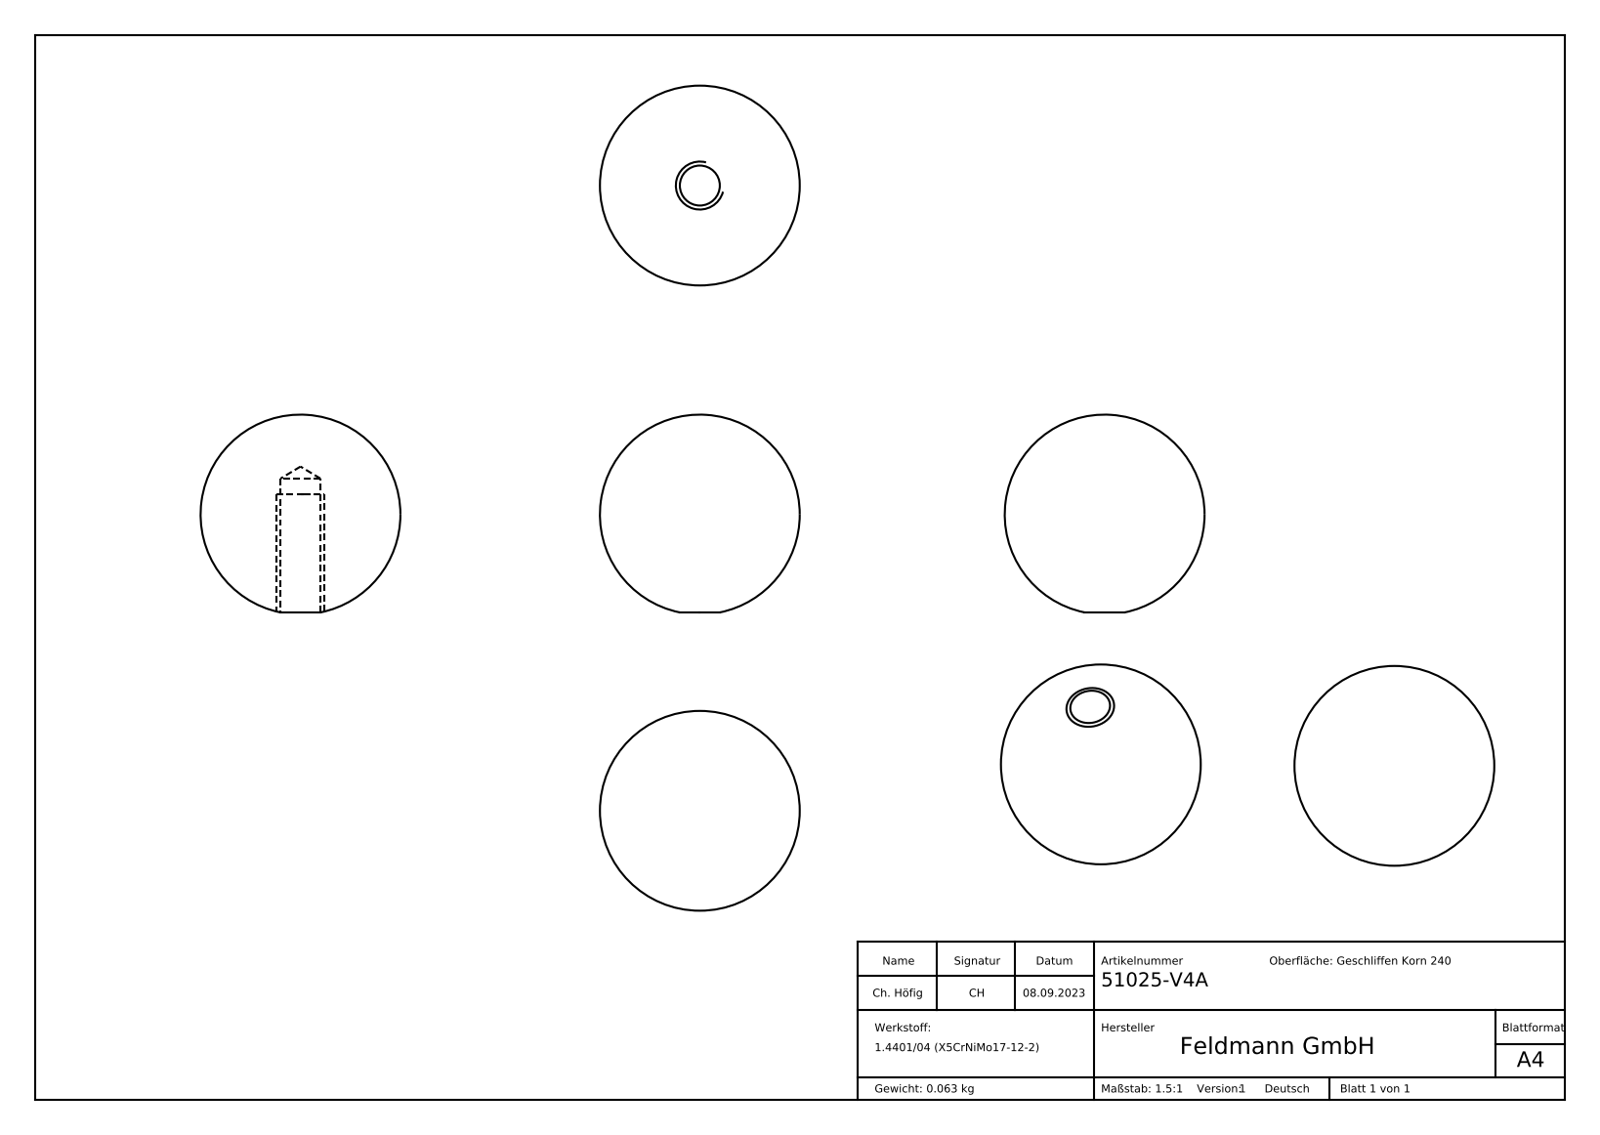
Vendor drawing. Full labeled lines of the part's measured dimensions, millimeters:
Part name (STEP PRODUCT): 51025-V4A
STEP written by: SolidWorks 2018 (CONFIG_CONTROL_DESIGN)
Units: millimetres
Bodies: 1 solid, 3 faces (0 planar, 1 cylindrical, 2 other)
Overall size (bounding box): 25 × 25 × 24.75
Volume: 7 840 mm³ · Surface area: 2 230 mm²
Round holes (diameter × count): ⌀5 ×1
